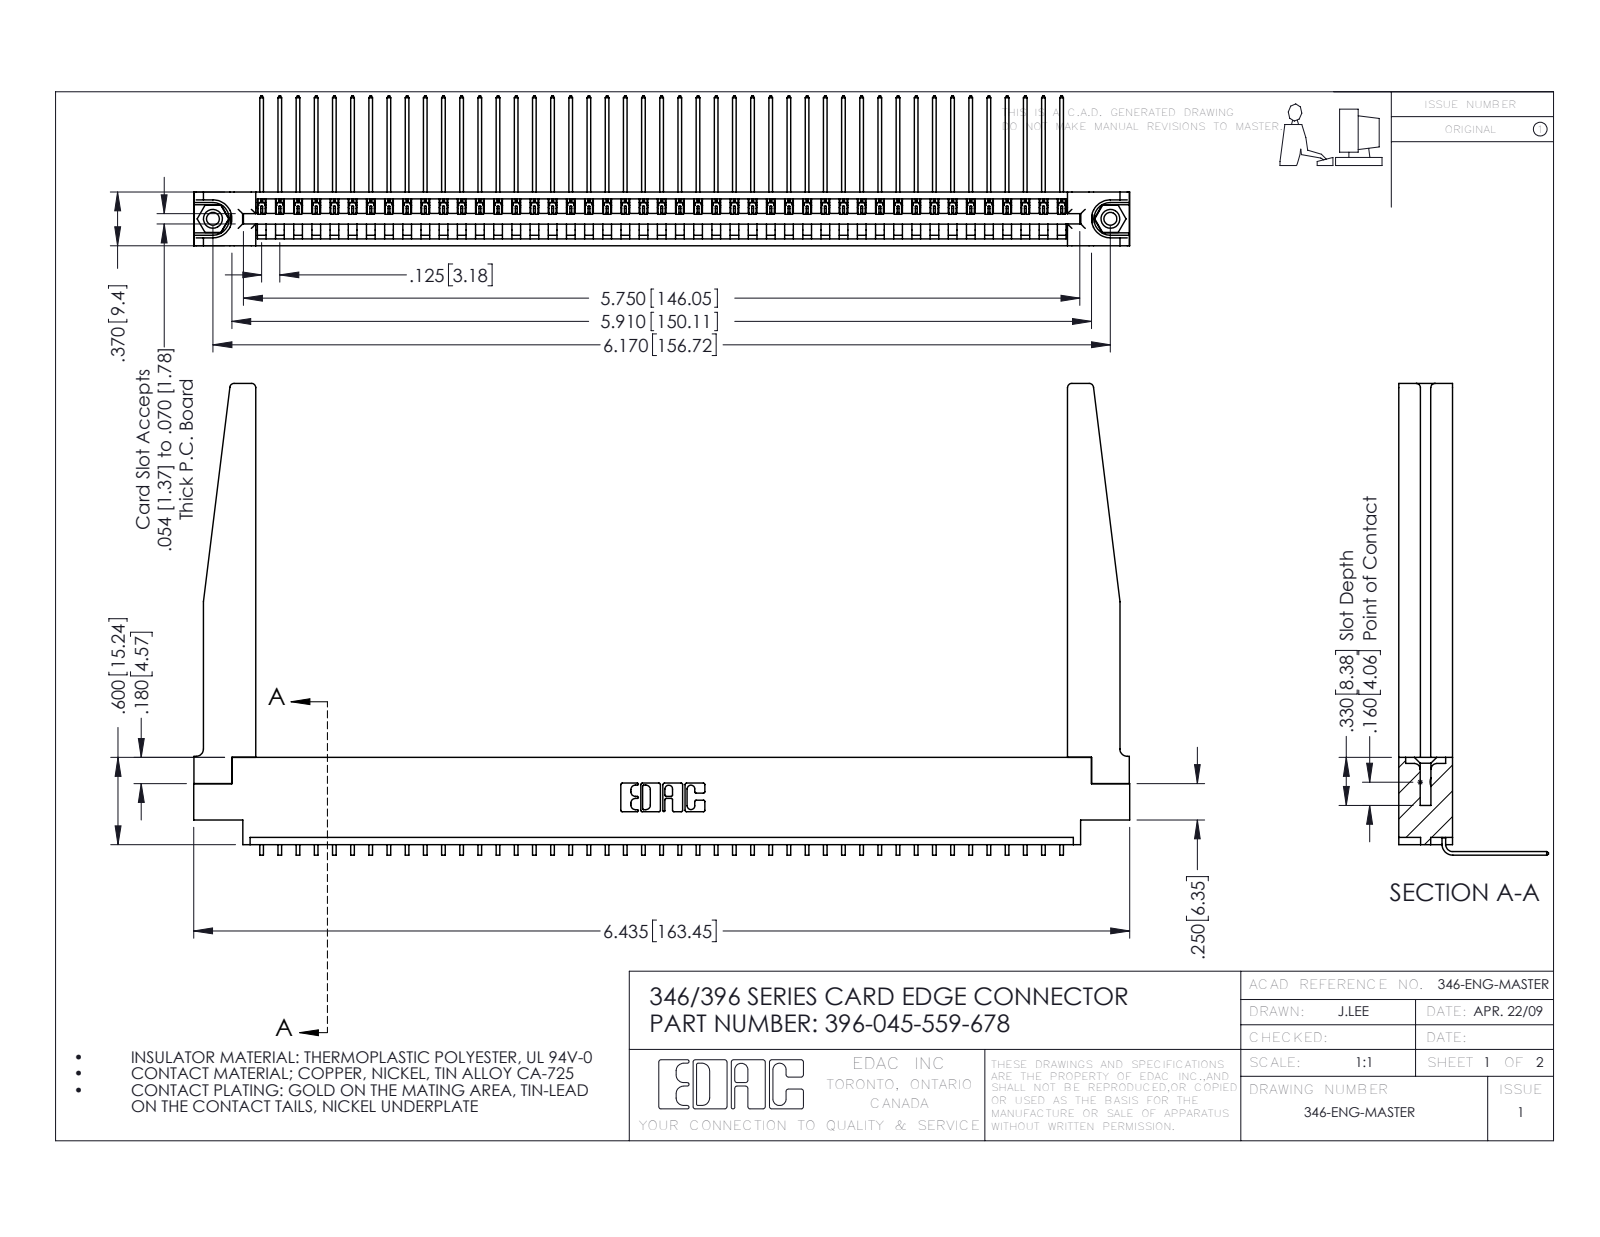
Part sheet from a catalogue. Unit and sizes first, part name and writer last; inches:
Units: inches
Overall size (bounding box): 6.435 × 3.243 × 1.03
Round holes (diameter × count): ⌀0.089 ×2, ⌀0.125 ×2, ⌀0.156 ×2, ⌀0.064 ×1
Round bosses / shafts (diameter × count): ⌀0.155 ×2
Partial cylindrical surfaces — rounded edges, fillets, slot ends (radius × count): R0.006 ×90, R0.01 ×22, R0.03 ×8, R0.007 ×6, R0.031 ×6, R0.026 ×3, R0.05 ×3, R0.031 ×2
Main face-to-face distances: 0.37, 0.048, 0.322, 0.072, 0.148, 0.025, 0.15, 0.25, 0.298, 0.222
Hole centre spacings: 0.246, 5.961, 6.17
Volume: 1.377 in³ · Surface area: 42.16 in²
Bodies: 50 solids, 3060 faces (2112 planar, 896 cylindrical, 52 other)
Part name (STEP PRODUCT): 346-220-078_345-220-078; 396-045-559-678; 346 Part_0.170 Offset - 0.156 Dia-TH; 345-250-001_345-250-001-102 (+1 more)
STEP written by: SolidWorks 2016 (CONFIG_CONTROL_DESIGN)
